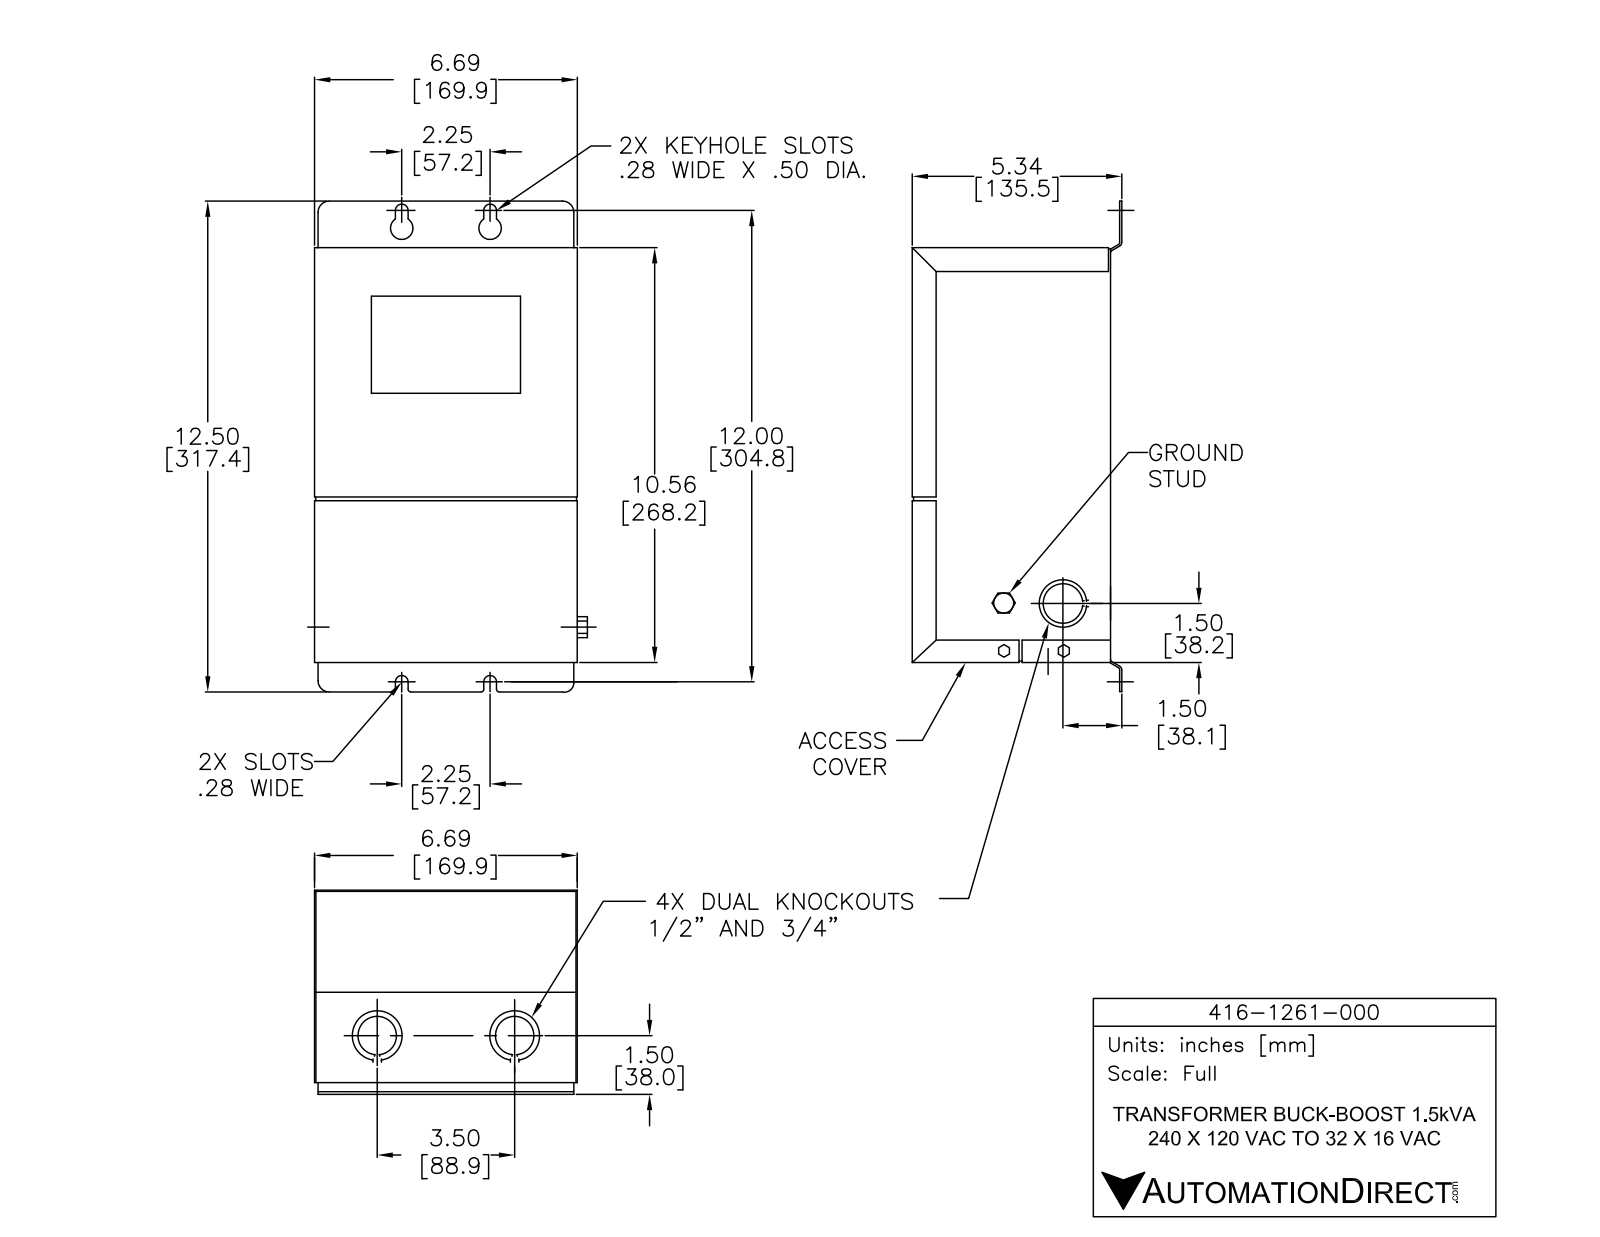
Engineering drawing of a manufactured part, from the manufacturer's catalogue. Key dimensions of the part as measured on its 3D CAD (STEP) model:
Part name (STEP PRODUCT): 416-1261-000
STEP written by: SolidWorks 2013 (AUTOMOTIVE_DESIGN)
Units: inches
Bodies: 1 solid, 186 faces (114 planar, 64 cylindrical, 8 other)
Overall size (bounding box): 12.5 × 6.9 × 5.341
Volume: 362.1 in³ · Surface area: 348.2 in²
Round holes (diameter × count): ⌀0.5 ×2, ⌀0.875 ×2, ⌀0.24 ×1, ⌀0.29 ×1, ⌀0.875 ×1
Round bosses / shafts (diameter × count): ⌀1.11 ×2, ⌀1.125 ×1
Partial cylindrical surfaces — rounded edges, fillets, slot ends (radius × count): R0.04 ×10, R0.25 ×10, R0.14 ×5, R0.08 ×2, R0.1 ×1, R0.167 ×1, R0.207 ×1
Main face-to-face distances: 5.12, 6.62, 0.04, 10.64, 6.66, 5.121, 6.7, 5.3, 0.18, 5.301
Hole centre spacings: 1.361, 1.371, 2.25, 2.35, 3.5
